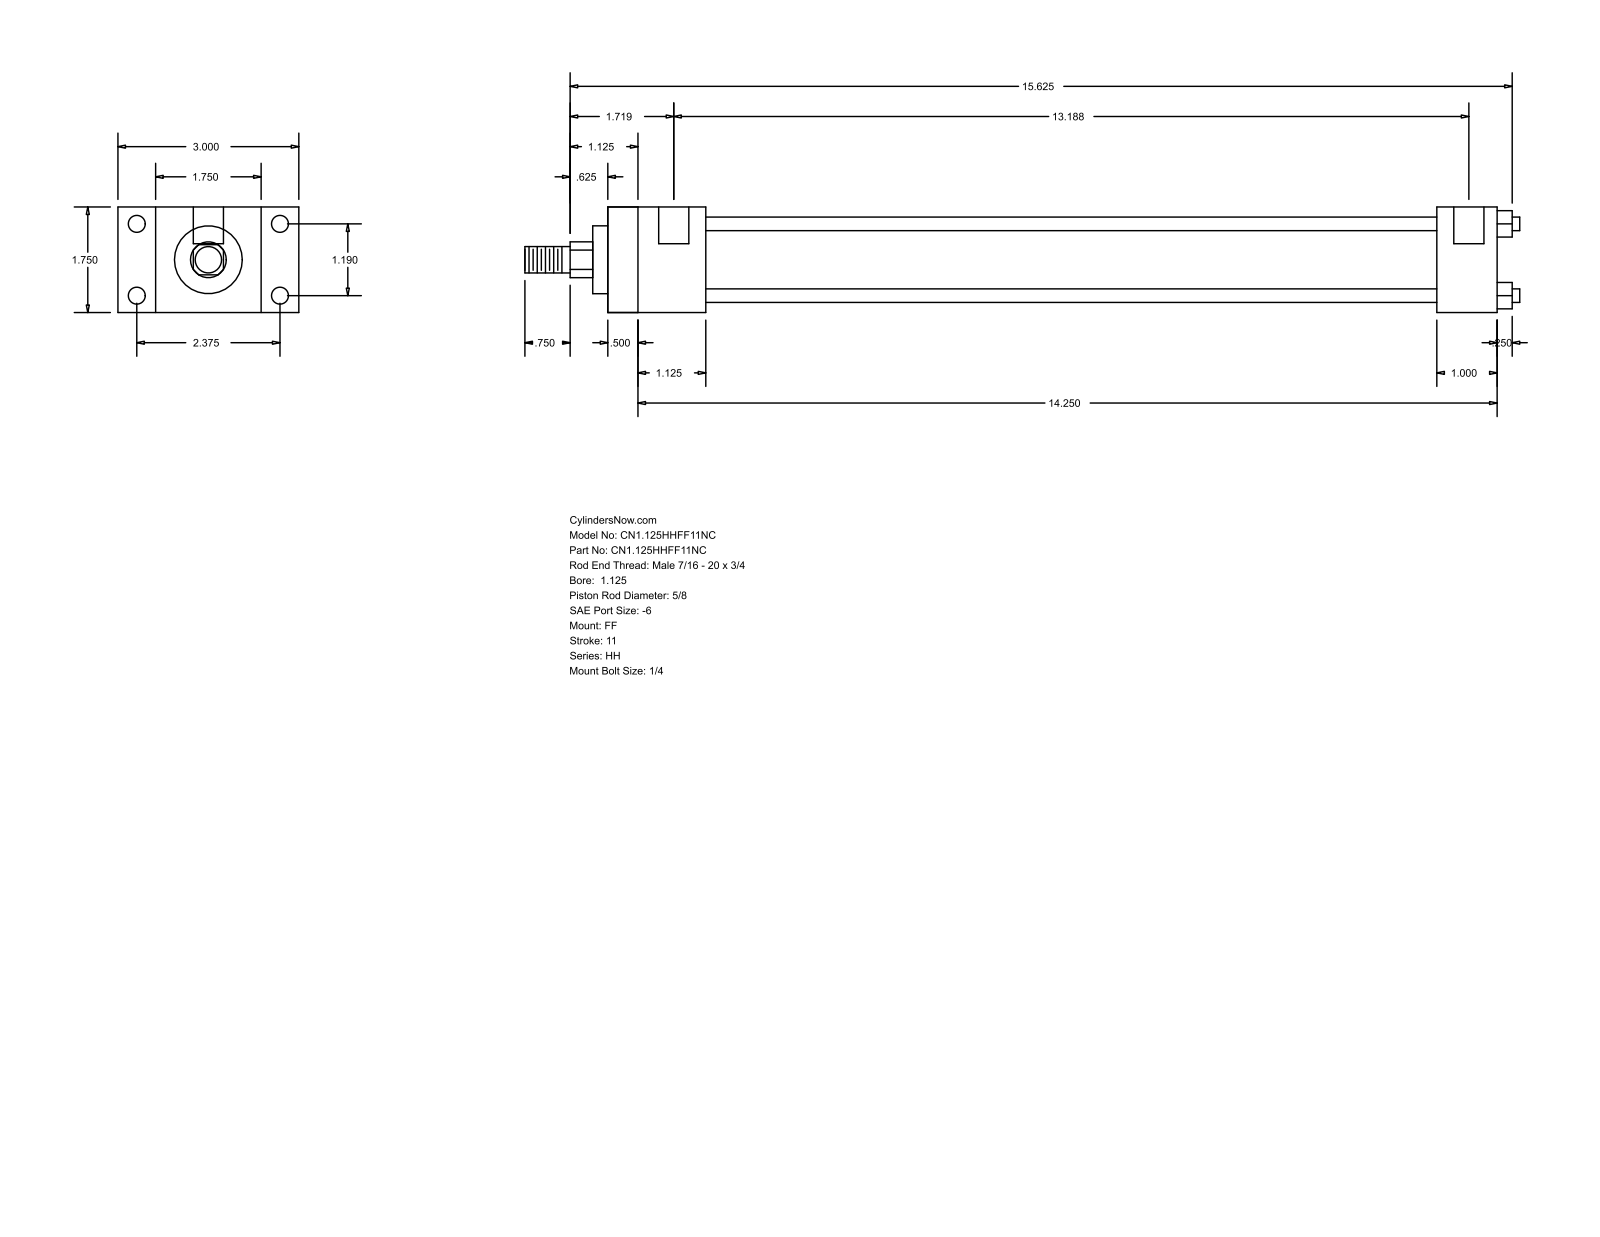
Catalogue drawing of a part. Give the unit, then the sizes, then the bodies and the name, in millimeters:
Units: millimetres
Overall size (bounding box): 419.1 × 76.2 × 44.45
Round holes (diameter × count): ⌀5.56 ×4, ⌀7.14 ×4, ⌀12.7 ×2
Round bosses / shafts (diameter × count): ⌀5.71 ×4, ⌀34.92 ×1, ⌀28.57 ×1, ⌀15.88 ×1, ⌀11.11 ×1
Partial cylindrical surfaces — rounded edges, fillets, slot ends (radius × count): R7.54 ×1
Main face-to-face distances: 44.46, 374.64, 15.87, 12.69, 361.95, 28.58, 60.33, 25.4, 41.27, 349.24
Hole centre spacings: 30.22, 60.32, 67.47, 331.79, 3.17, 334.96
Bodies: 0 solids, 92 faces (64 planar, 28 cylindrical, 0 other)
Part name (STEP PRODUCT): HH_FF__0112_0.625
STEP written by: GSSL Pune (CONFIG_CONTROL_DESIGN)
